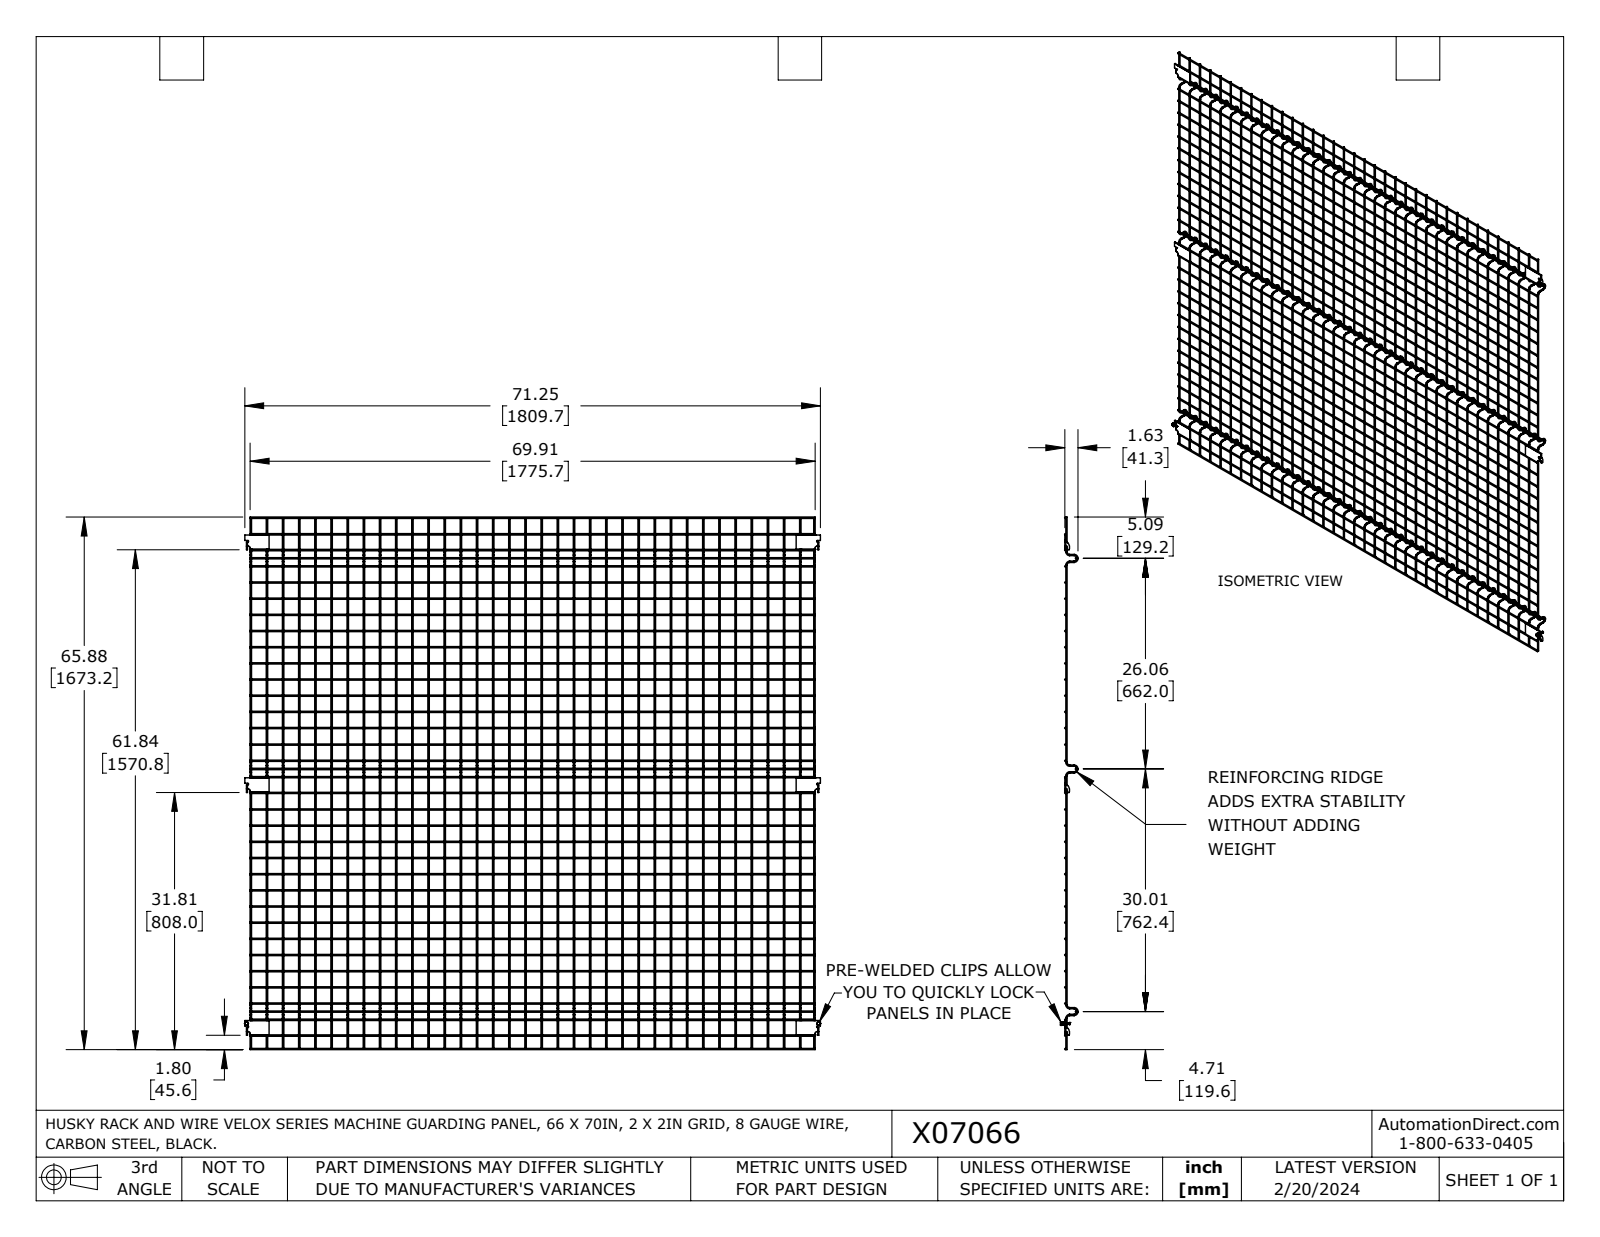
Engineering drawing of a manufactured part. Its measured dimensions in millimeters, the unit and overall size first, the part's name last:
Units: millimetres
Overall size (bounding box): 1811.4 × 1673.2 × 53.4
Round holes (diameter × count): ⌀5.1 ×2, ⌀6.4 ×2
Round bosses / shafts (diameter × count): ⌀4.1 ×325, ⌀9.9 ×2, ⌀6.2 ×2, ⌀4.7 ×2
Partial cylindrical surfaces — rounded edges, fillets, slot ends (radius × count): R2.5 ×6, R5.5 ×6, R6.4 ×3, R22 ×3, R0.2 ×2, R1.7 ×2, R3.4 ×2
Main face-to-face distances: 3.4, 3.2, 44.8, 762.8, 11.9, 1787.6, 762.4, 1525.2, 71.1, 1728.4
Hole centre spacings: 1798.5
Volume: 1 771 000 mm³ · Surface area: 1 727 000 mm²
Bodies: 83 solids, 1263 faces (254 planar, 553 cylindrical, 456 other)
Part name (STEP PRODUCT): X07066
STEP written by: SolidWorks 2023 (AUTOMOTIVE_DESIGN)
